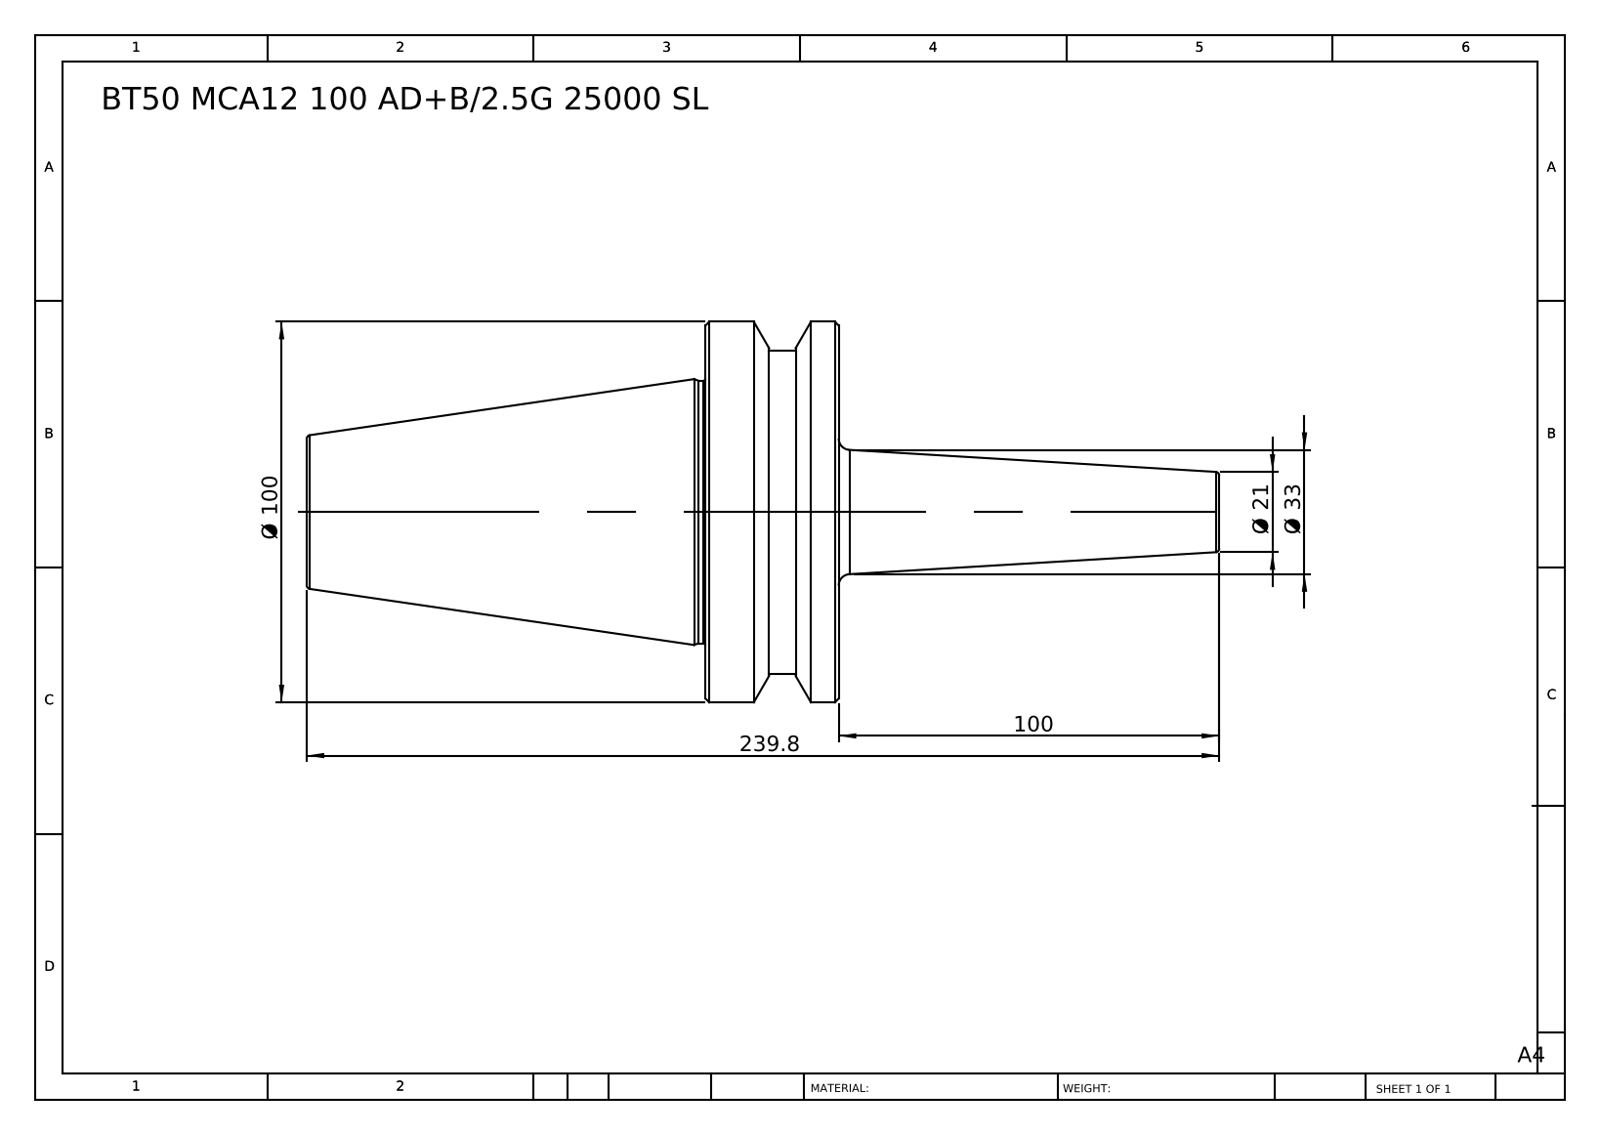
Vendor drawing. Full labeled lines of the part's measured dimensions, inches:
Part name (STEP PRODUCT): BT50 MCA12 100 AD+B-2.5G 25000 SL
STEP written by: SolidWorks 2014 (CONFIG_CONTROL_DESIGN)
Units: inches
Bodies: 1 solid, 36 faces (6 planar, 8 cylindrical, 22 other)
Overall size (bounding box): 9.441 × 3.937 × 3.937
Volume: 34.69 in³ · Surface area: 80.93 in²
Round bosses / shafts (diameter × count): ⌀3.937 ×1, ⌀3.346 ×1, ⌀2.717 ×1
Main face-to-face distances: 1.378, 5.504, 4.126, 3.937, 5.315, 9.441, 4.382, 0.445, 0.933, 5.059
